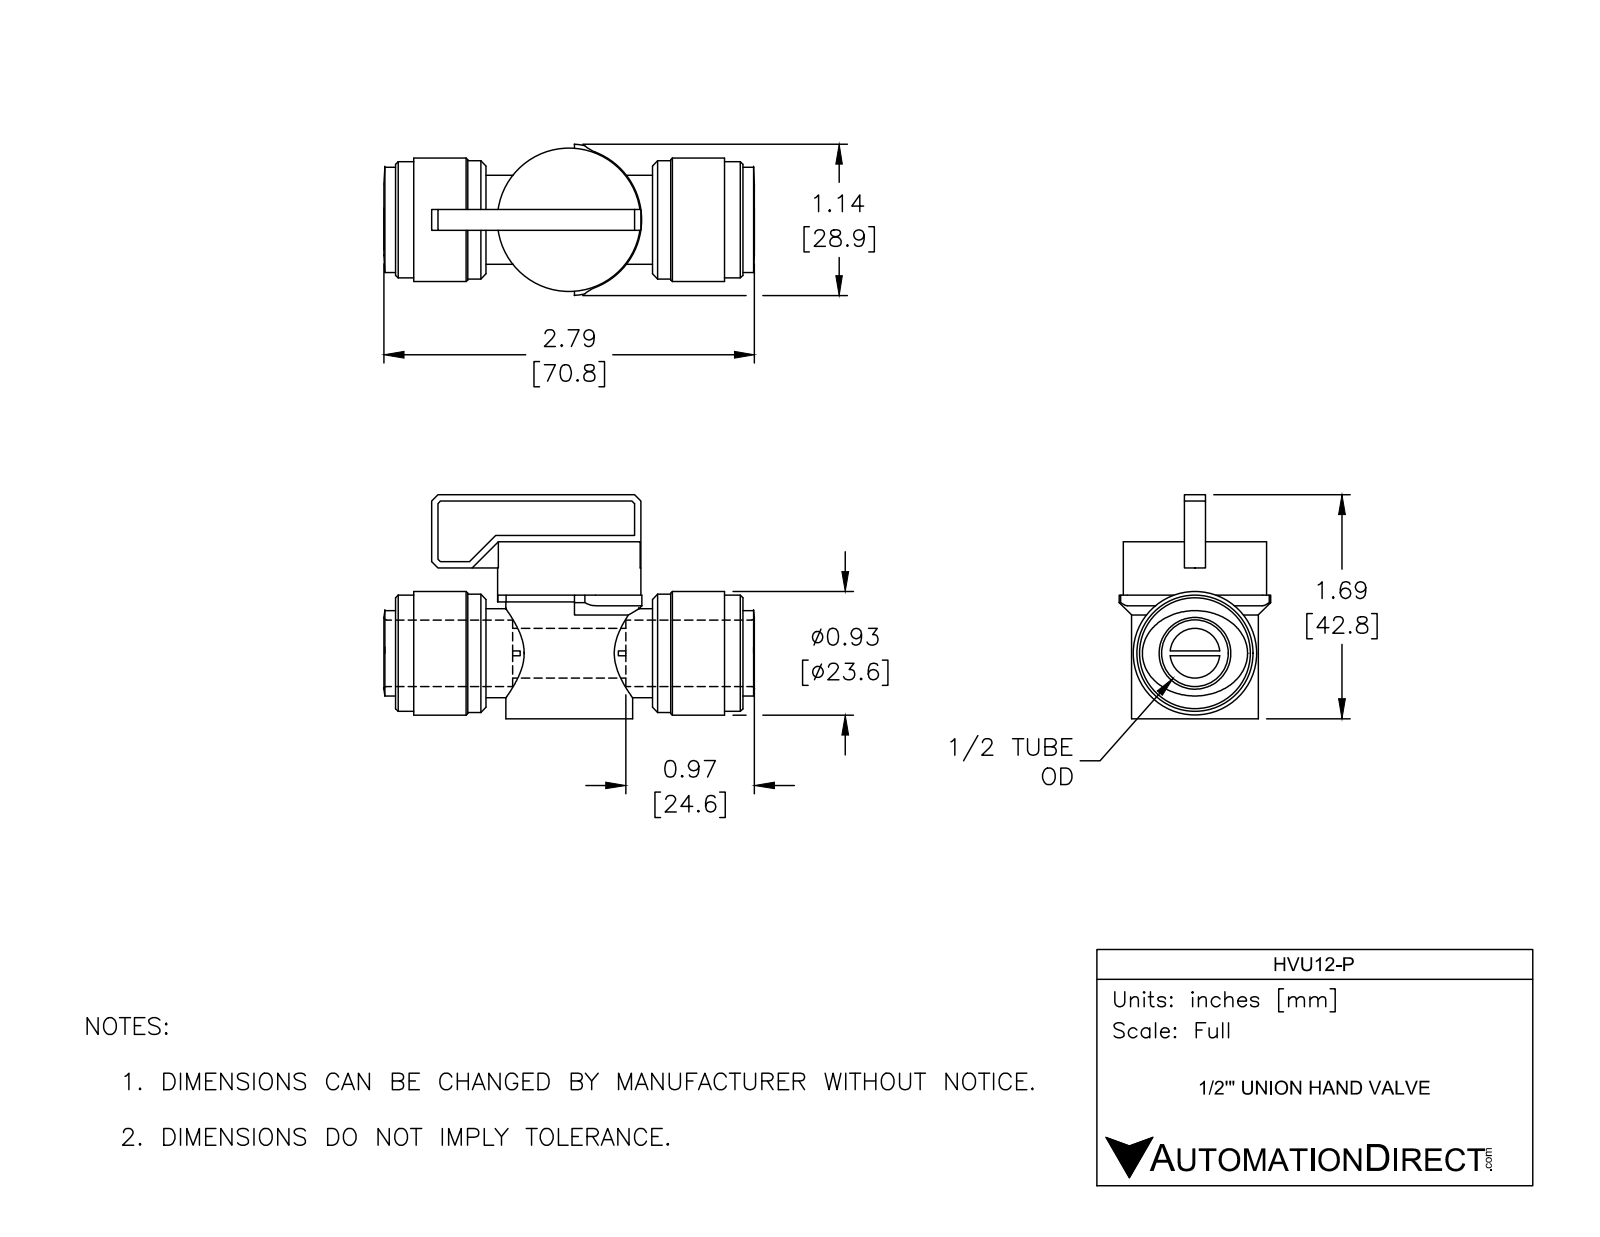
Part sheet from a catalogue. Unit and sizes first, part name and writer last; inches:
Units: inches
Overall size (bounding box): 2.787 × 1.685 × 1.139
Round holes (diameter × count): ⌀0.374 ×1, ⌀0.5 ×1
Round bosses / shafts (diameter × count): ⌀1.079 ×1, ⌀0.953 ×1, ⌀0.929 ×1, ⌀0.89 ×1, ⌀0.874 ×1, ⌀0.669 ×1
Partial cylindrical surfaces — rounded edges, fillets, slot ends (radius × count): R0.276 ×2, R0.547 ×1, R0.571 ×1
Main face-to-face distances: 1.331, 0.071, 0.114, 0.043, 1.933, 0.047, 0.681, 1.685, 0.354, 0.307
Volume: 1.711 in³ · Surface area: 17.98 in²
Bodies: 1 solid, 121 faces (64 planar, 32 cylindrical, 25 other)
Part name (STEP PRODUCT): HVU12-P
STEP written by: SolidWorks 2017 (AUTOMOTIVE_DESIGN)
